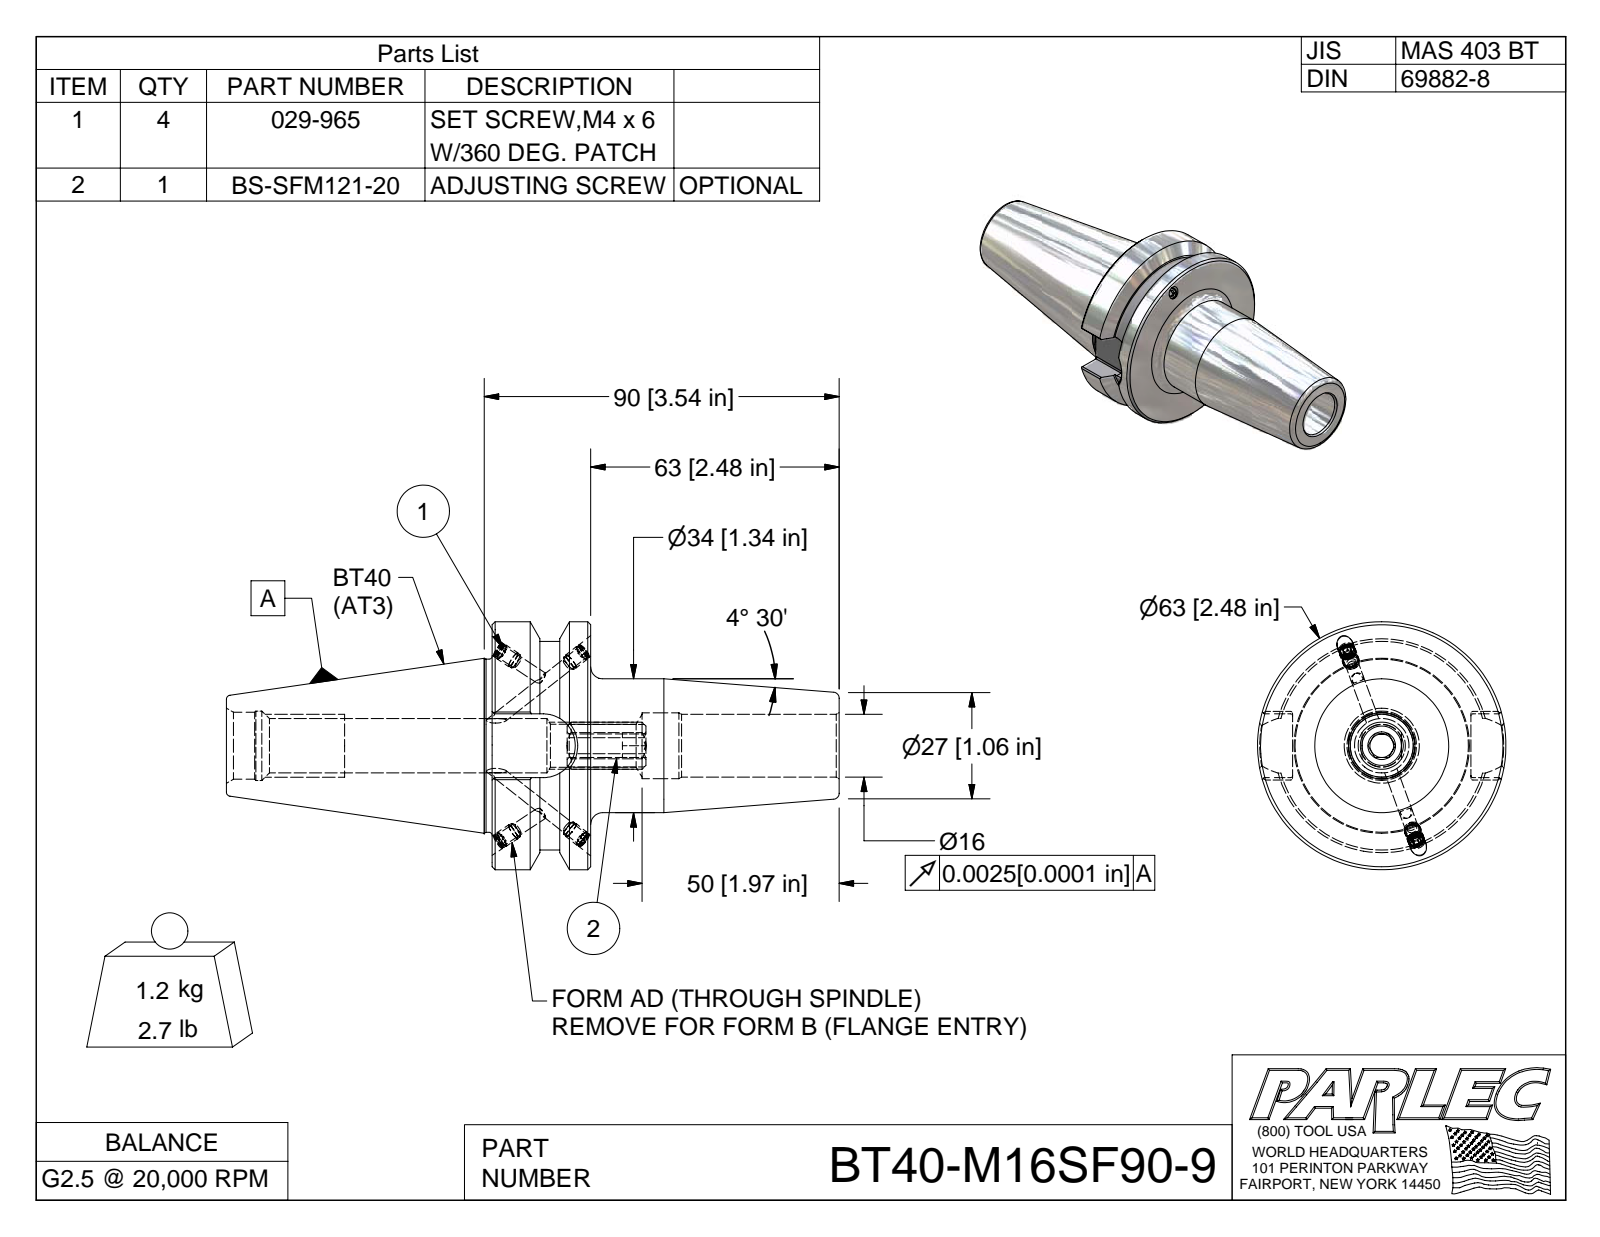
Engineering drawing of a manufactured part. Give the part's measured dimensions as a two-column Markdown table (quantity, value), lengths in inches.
| quantity | value |
| --- | --- |
| part name | BT40-M16SF90-9; BT40BC-M16SF90-9-1; 029-965; BS-SFM121-20 |
| STEP written by | Autodesk Inventor 2009 (AUTOMOTIVE_DESIGN) |
| units | inches |
| bodies | 6 solids, 173 faces (79 planar, 43 cylindrical, 51 other) |
| overall size | 6.118 × 2.48 × 2.48 |
| volume | 9.705 in³ |
| surface area | 51.98 in² |
| round holes (diameter × count) | 0.13 × 4, 0.161 × 4, 0.629 × 1, 0.659 × 1, 0.694 × 1 |
| round bosses / shafts (diameter × count) | 0.165 × 4, 0.157 × 4, 2.48 × 1, 2.087 × 1, 1.75 × 1, 1.73 × 1, 1.339 × 1 |
| partial cylindrical surfaces (radius × count) | 0.02 × 8, 0.236 × 1, 0.319 × 1 |
| main face-to-face distances | 0.984, 1.78, 0.693, 1.087, 3.465, 2.481, 2.653, 3.637, 6.119, 0.637 |
